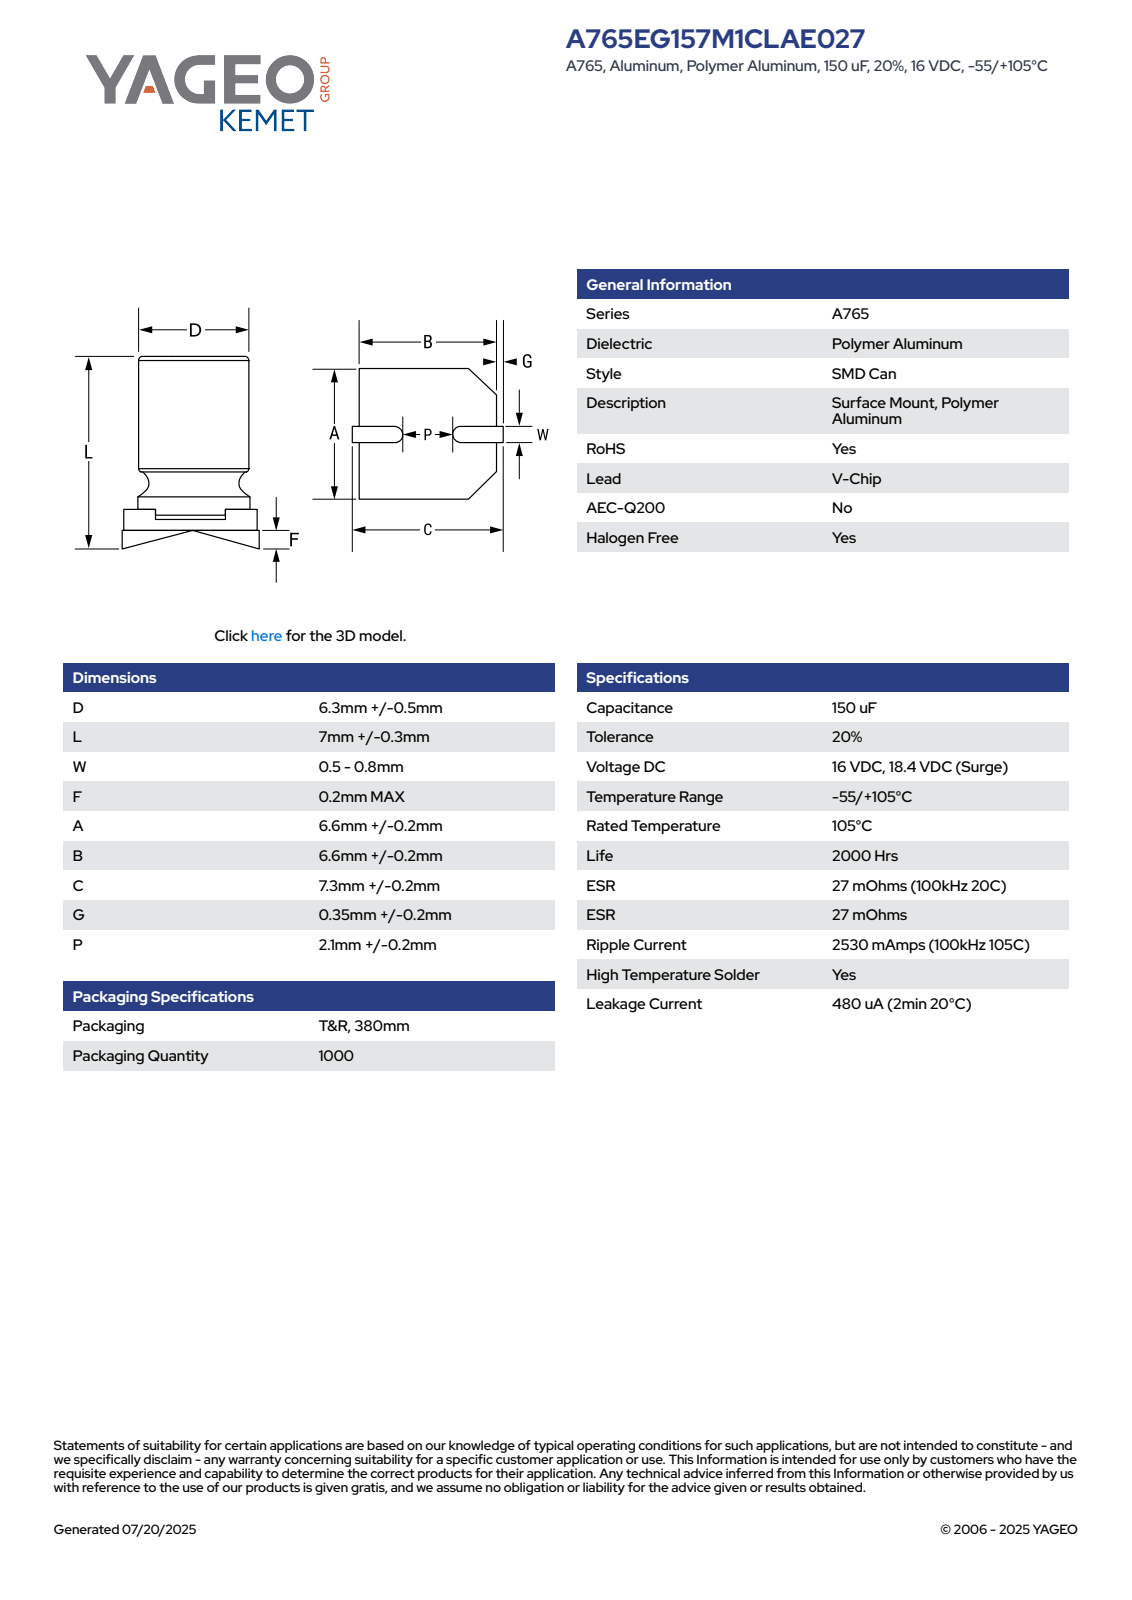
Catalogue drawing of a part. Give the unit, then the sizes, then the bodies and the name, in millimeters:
Units: millimetres
Overall size (bounding box): 7.5 × 7.3 × 6.8
Round bosses / shafts (diameter × count): ⌀6.5 ×1
Partial cylindrical surfaces — rounded edges, fillets, slot ends (radius × count): R0.2 ×2, R2.7 ×1, R3.4 ×1
Main face-to-face distances: 0.37, 7.1, 6.73, 6.8, 1.82, 1.45, 5.28, 2.02, 0.57, 7.3
Volume: 245 mm³ · Surface area: 342 mm²
Bodies: 5 solids, 76 faces (59 planar, 11 cylindrical, 6 other)
Part name (STEP PRODUCT): CAC_KS_6.3X7_D6.8L7.3W0.8F0.2A6.8B6.8C7.5P2.3
STEP written by: SolidWorks 2014 (AUTOMOTIVE_DESIGN)
